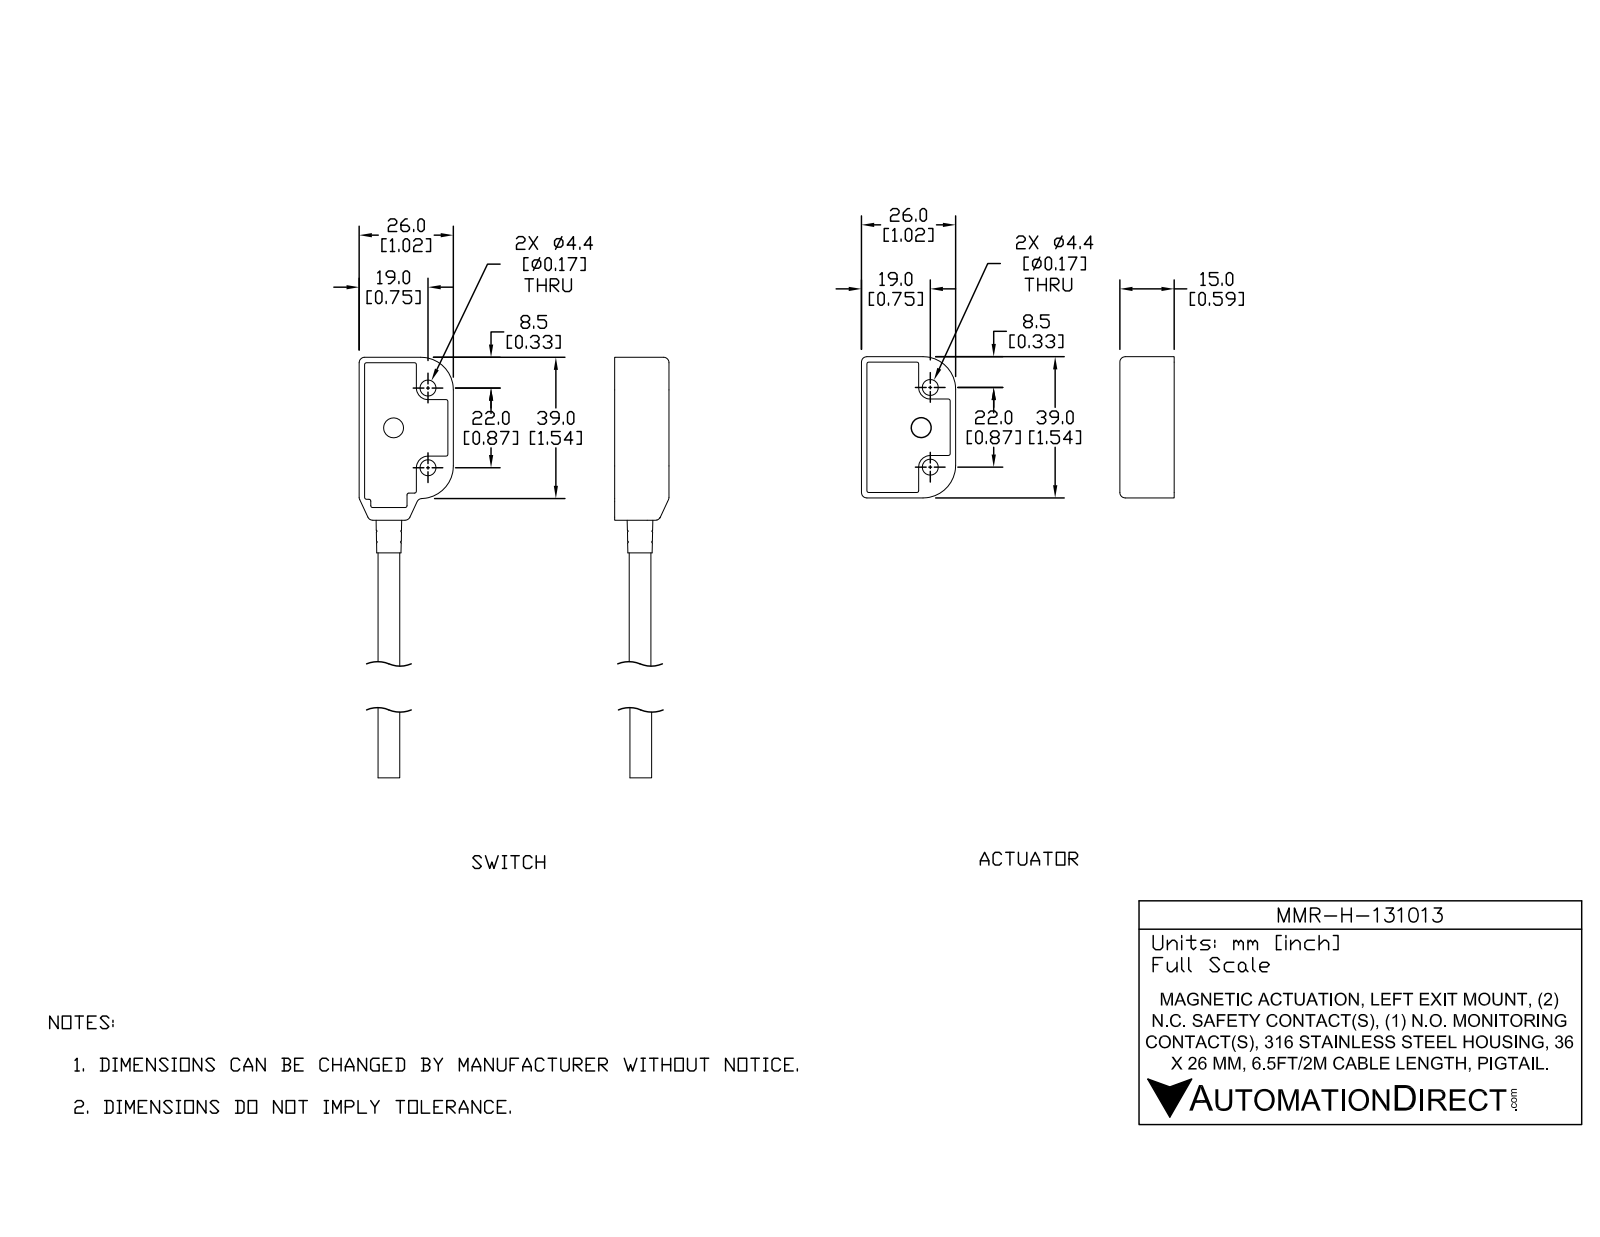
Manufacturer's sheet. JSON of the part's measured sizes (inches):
{"part_name": "MMR-H-131013; MMR-H-131013_2; MMR-H-131013_1", "step_written_by": "SolidWorks 2017 (AUTOMOTIVE_DESIGN)", "units": "inches", "bodies": {"solids": 8, "faces": 590, "planar": 175, "cylindrical": 226, "other": 189}, "overall_size": [7.803, 2.087, 0.591], "volume_in3": 1.231, "surface_area_in2": 30.87, "round_holes": [[0.173, 4], [0.197, 2], [0.118, 1], [0.232, 1], [0.283, 1]], "round_bosses_or_shafts": [[0.079, 2], [0.339, 1], [0.299, 1], [0.28, 1], [0.236, 1]], "partial_cylinders_radius": [[0.02, 83], [0.012, 26], [0.059, 15], [0.008, 8], [0.157, 6], [0.126, 4], [0.13, 4], [0.181, 4]], "face_to_face_distances": [0.059, 0.575, 0.516, 0.098, 0.461, 0.52, 0.055, 0.591, 0.531, 0.965], "hole_center_spacings": [0.572, 0.866, 1.239, 1.535, 1.763, 0.076, 0.44, 0.448]}
